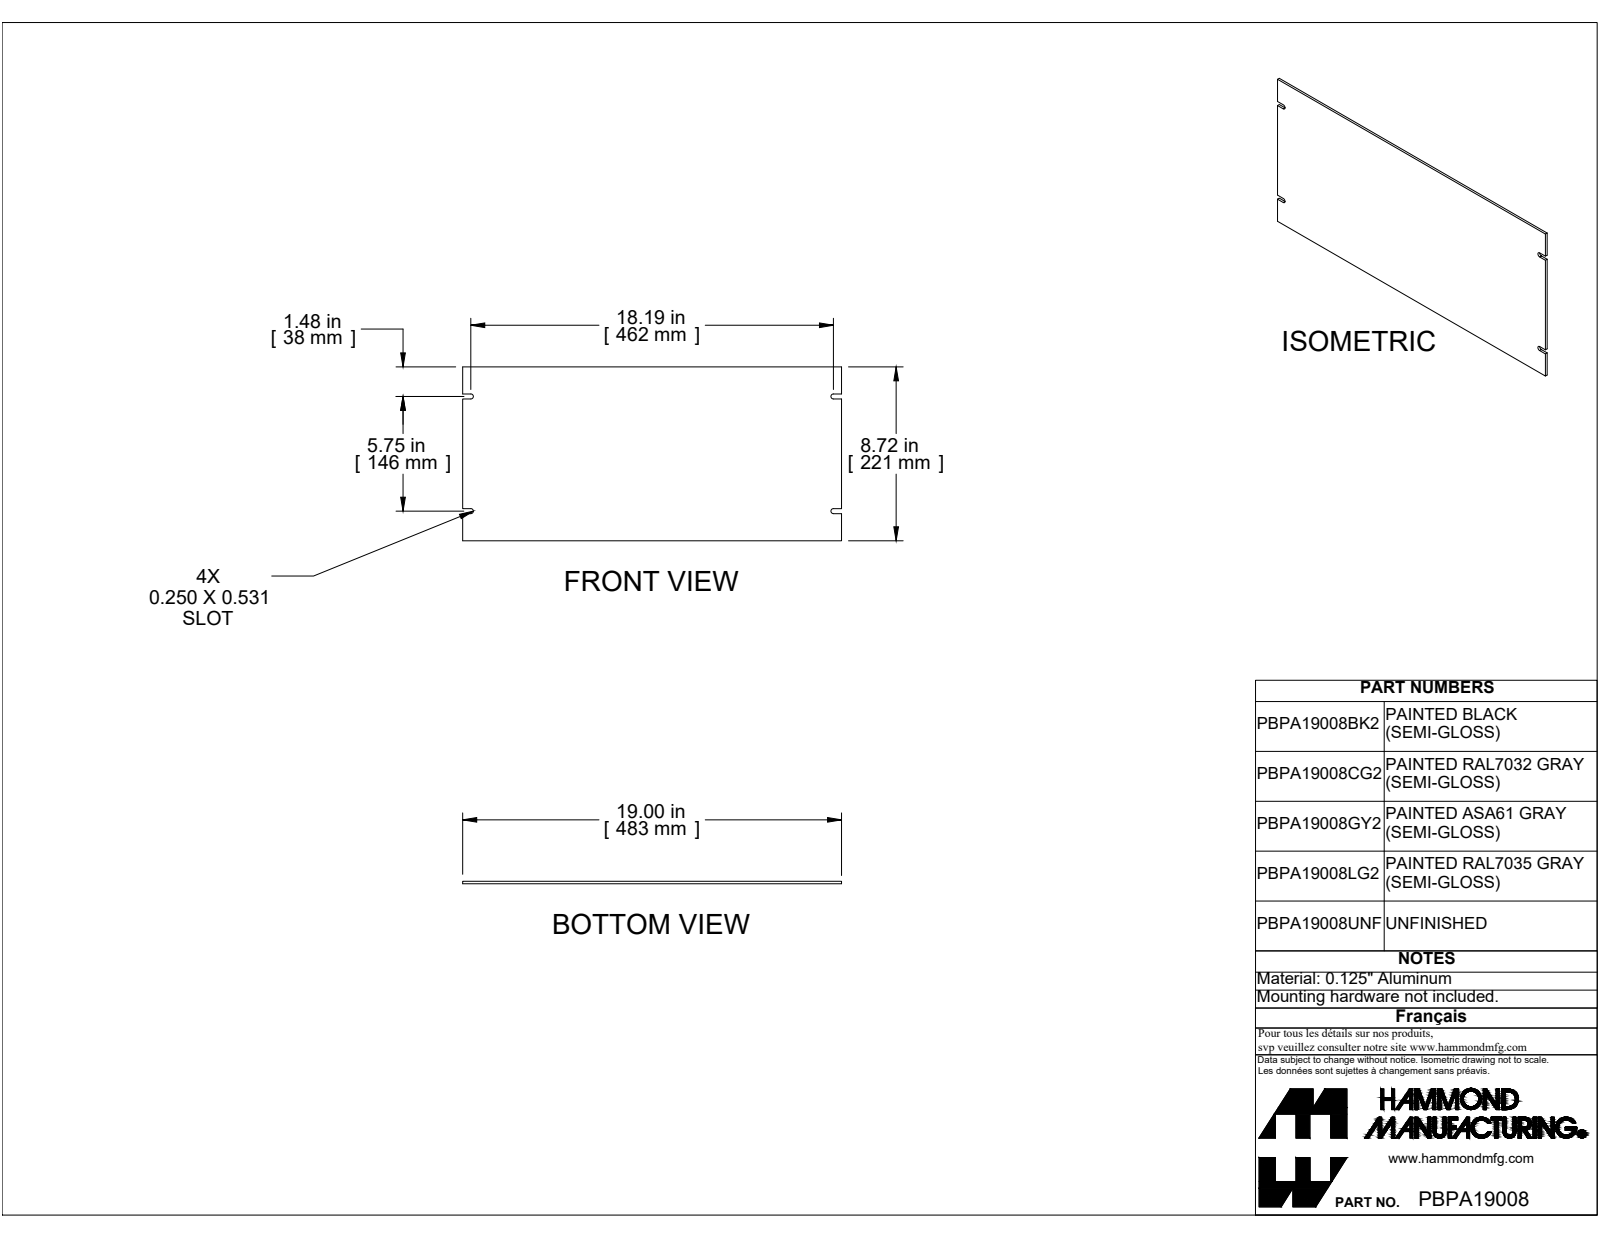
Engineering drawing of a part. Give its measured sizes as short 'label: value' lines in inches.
name: PBPA19008BK2
written by: SolidWorks 2019 (CONFIG_CONTROL_DESIGN)
unit: in
bodies: 1 solid, 22 faces (18 planar, 4 cylindrical, 0 other)
size: 19 × 8.718 × 0.125
volume: 20.64 in³; area: 337.7 in²
rounds: 4× R0.125
face distances: 0.125, 8.718, 19, 1.359, 1.609, 7.109, 7.359, 5.75, 0.25, 6
